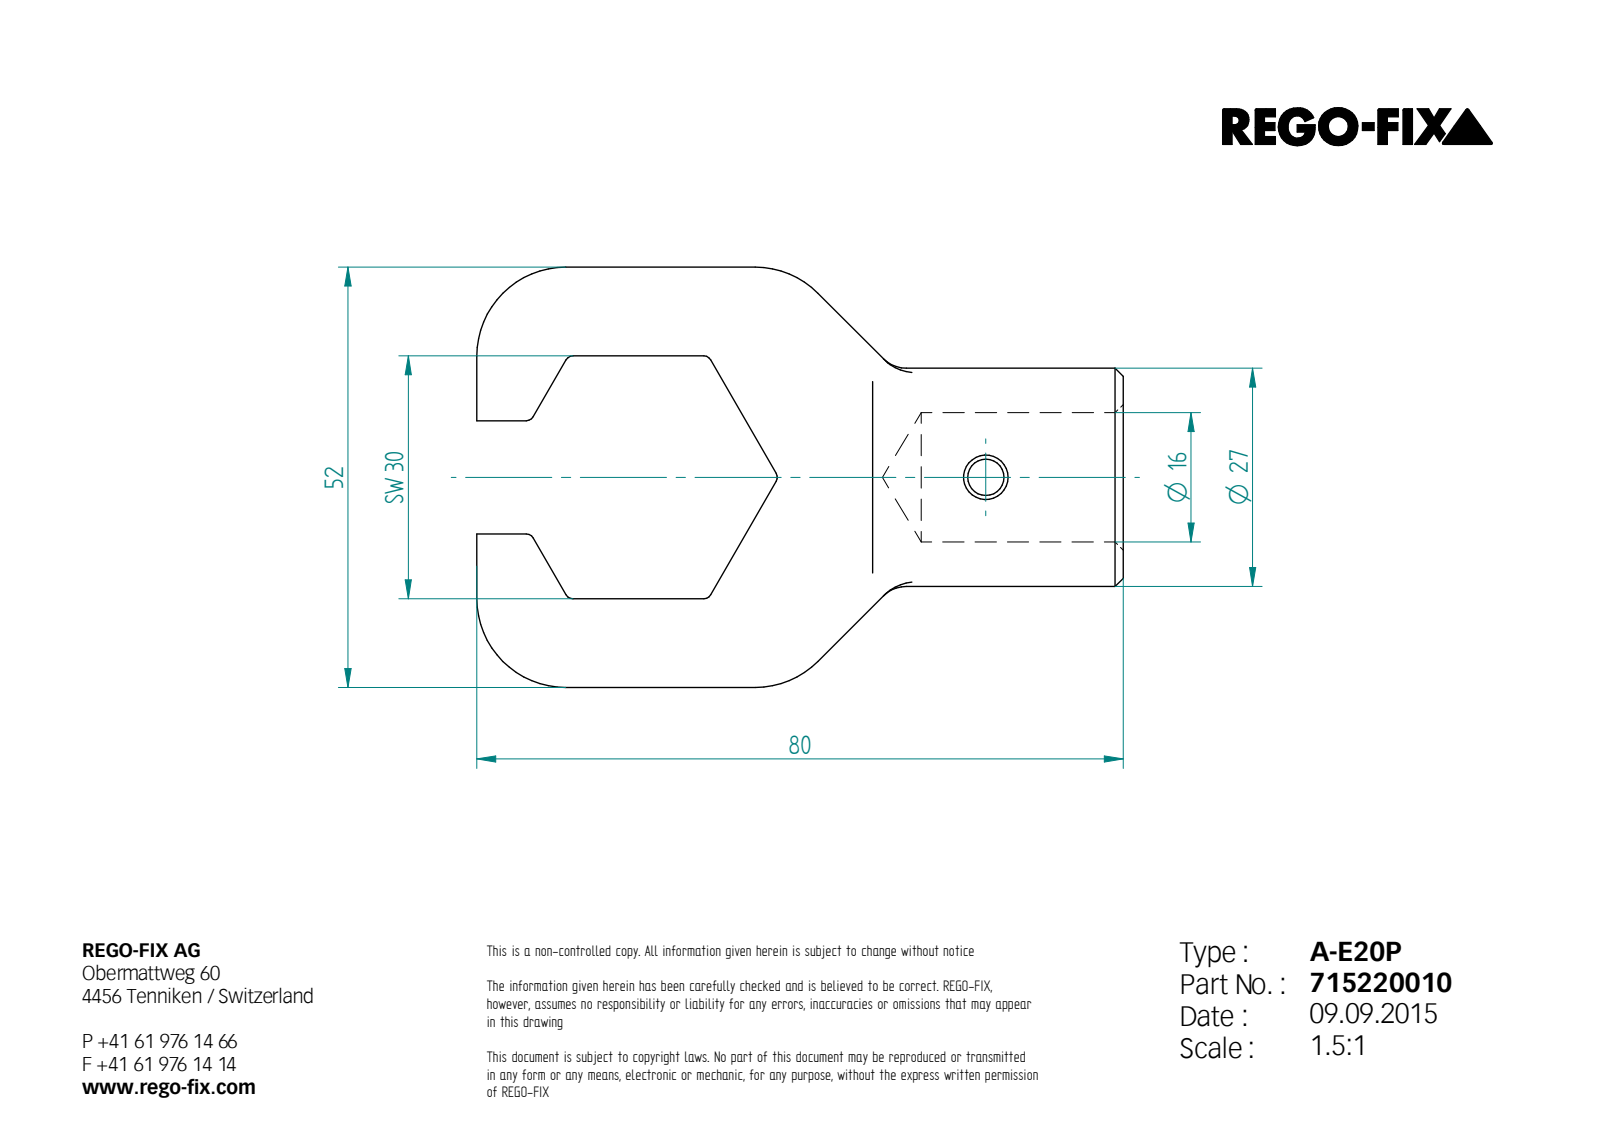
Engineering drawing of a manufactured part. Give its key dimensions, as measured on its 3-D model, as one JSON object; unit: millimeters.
{"step_written_by": "Unknown (AUTOMOTIVE_DESIGN)", "units": "millimeters", "bodies": {"solids": 1, "faces": 53, "planar": 19, "cylindrical": 22, "other": 12}, "overall_size": [80, 52, 27], "volume_mm3": 21384, "surface_area_mm2": 9399, "round_holes": [[4.5, 1], [5.5, 1], [16, 1]], "round_bosses_or_shafts": [[27, 1]], "partial_cylinders_radius": [[1, 13], [11, 4]], "face_to_face_distances": [6, 31, 10.97, 41.03, 52, 30.04, 30.06, 49, 80, 19]}
